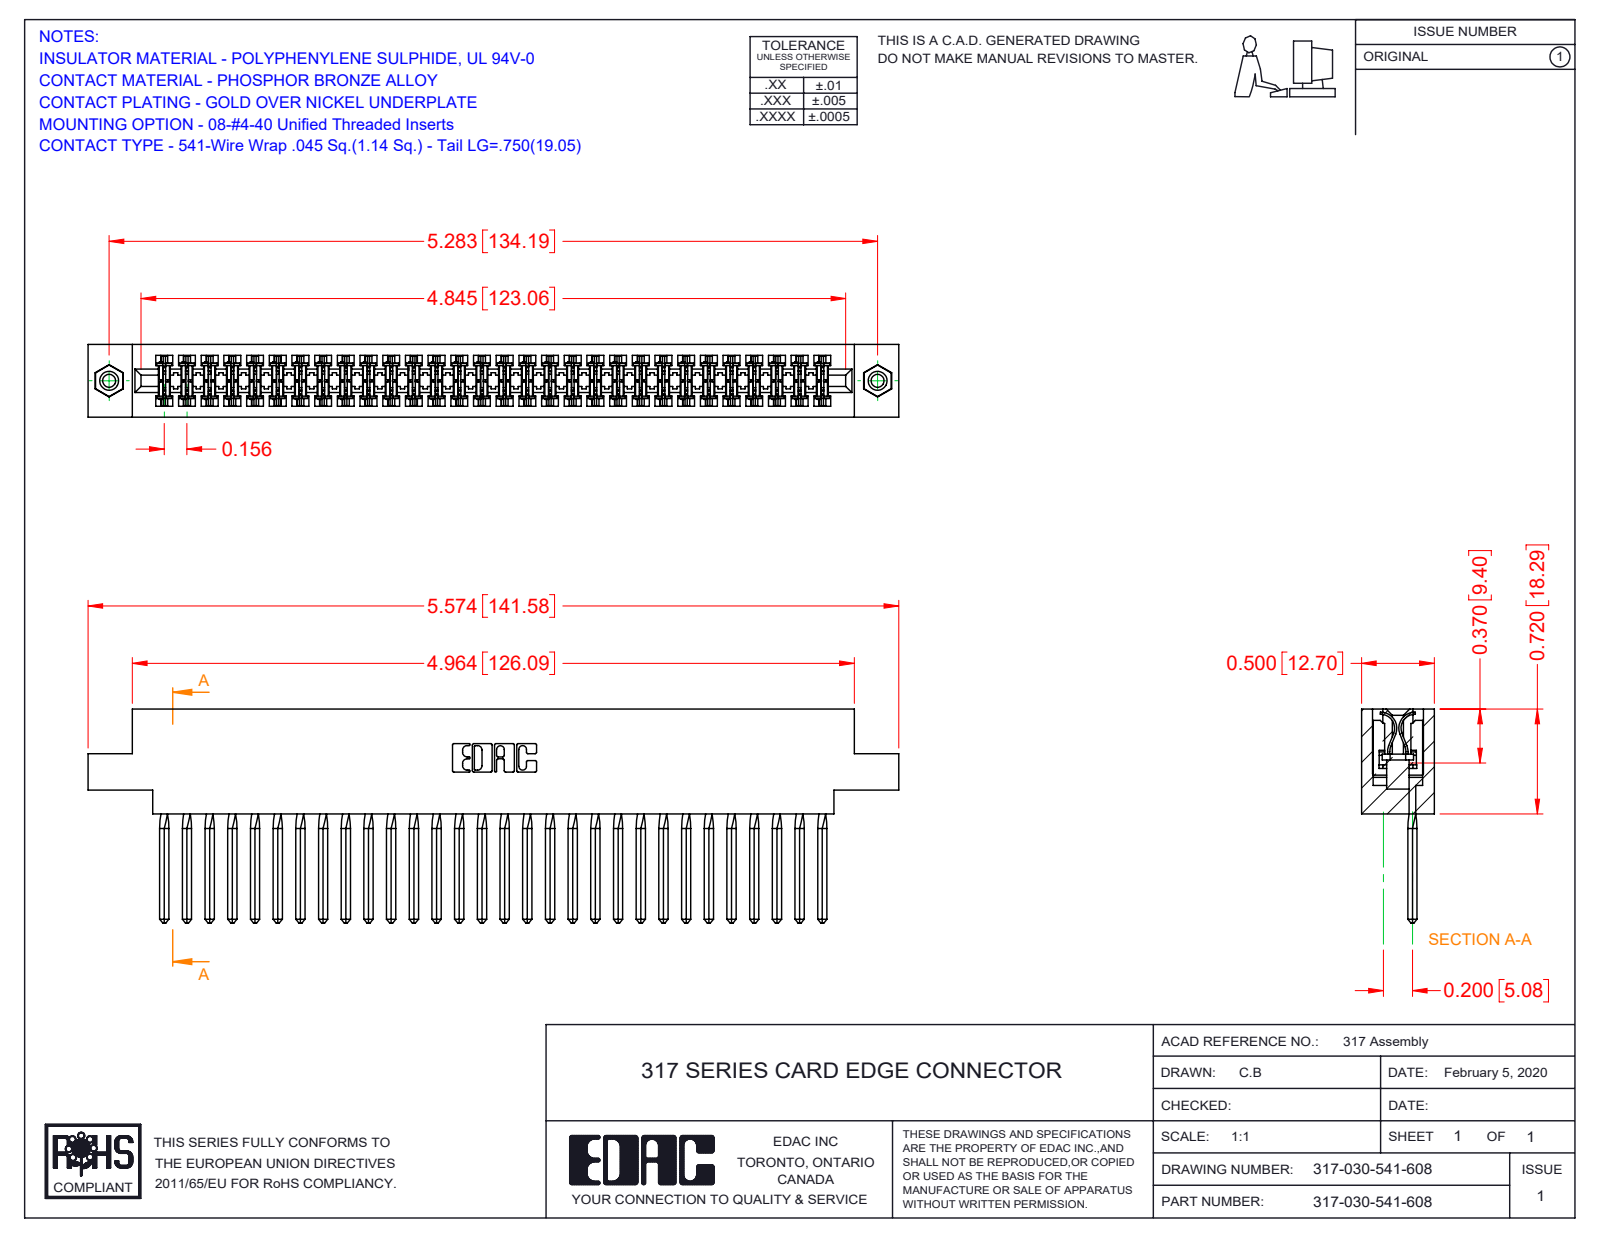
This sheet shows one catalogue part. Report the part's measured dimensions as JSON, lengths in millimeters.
{"part_name": "317-290-002_541; 317 Part_.156 Dia - TI; 345-250-001_345-250-003-102; 317-030-541-678", "step_written_by": "SolidWorks 2016 (CONFIG_CONTROL_DESIGN)", "units": "millimeters", "bodies": {"solids": 33, "faces": 4722, "planar": 3810, "cylindrical": 776, "other": 136}, "overall_size": [141.6, 37.3, 12.7], "volume_mm3": 22580, "surface_area_mm2": 31540, "round_holes": [[2.3, 2], [3.2, 2], [4, 2]], "round_bosses_or_shafts": [[3.9, 2]], "partial_cylinders_radius": [[0.4, 60], [0.3, 22], [0.2, 6], [0.8, 6], [0.7, 3], [2.4, 2], [2.5, 2], [2.8, 2]], "face_to_face_distances": [12.7, 1.9, 10.8, 8.9, 2.8, 5, 18.3, 3.5, 2.9, 5.4], "hole_center_spacings": [134.2]}
